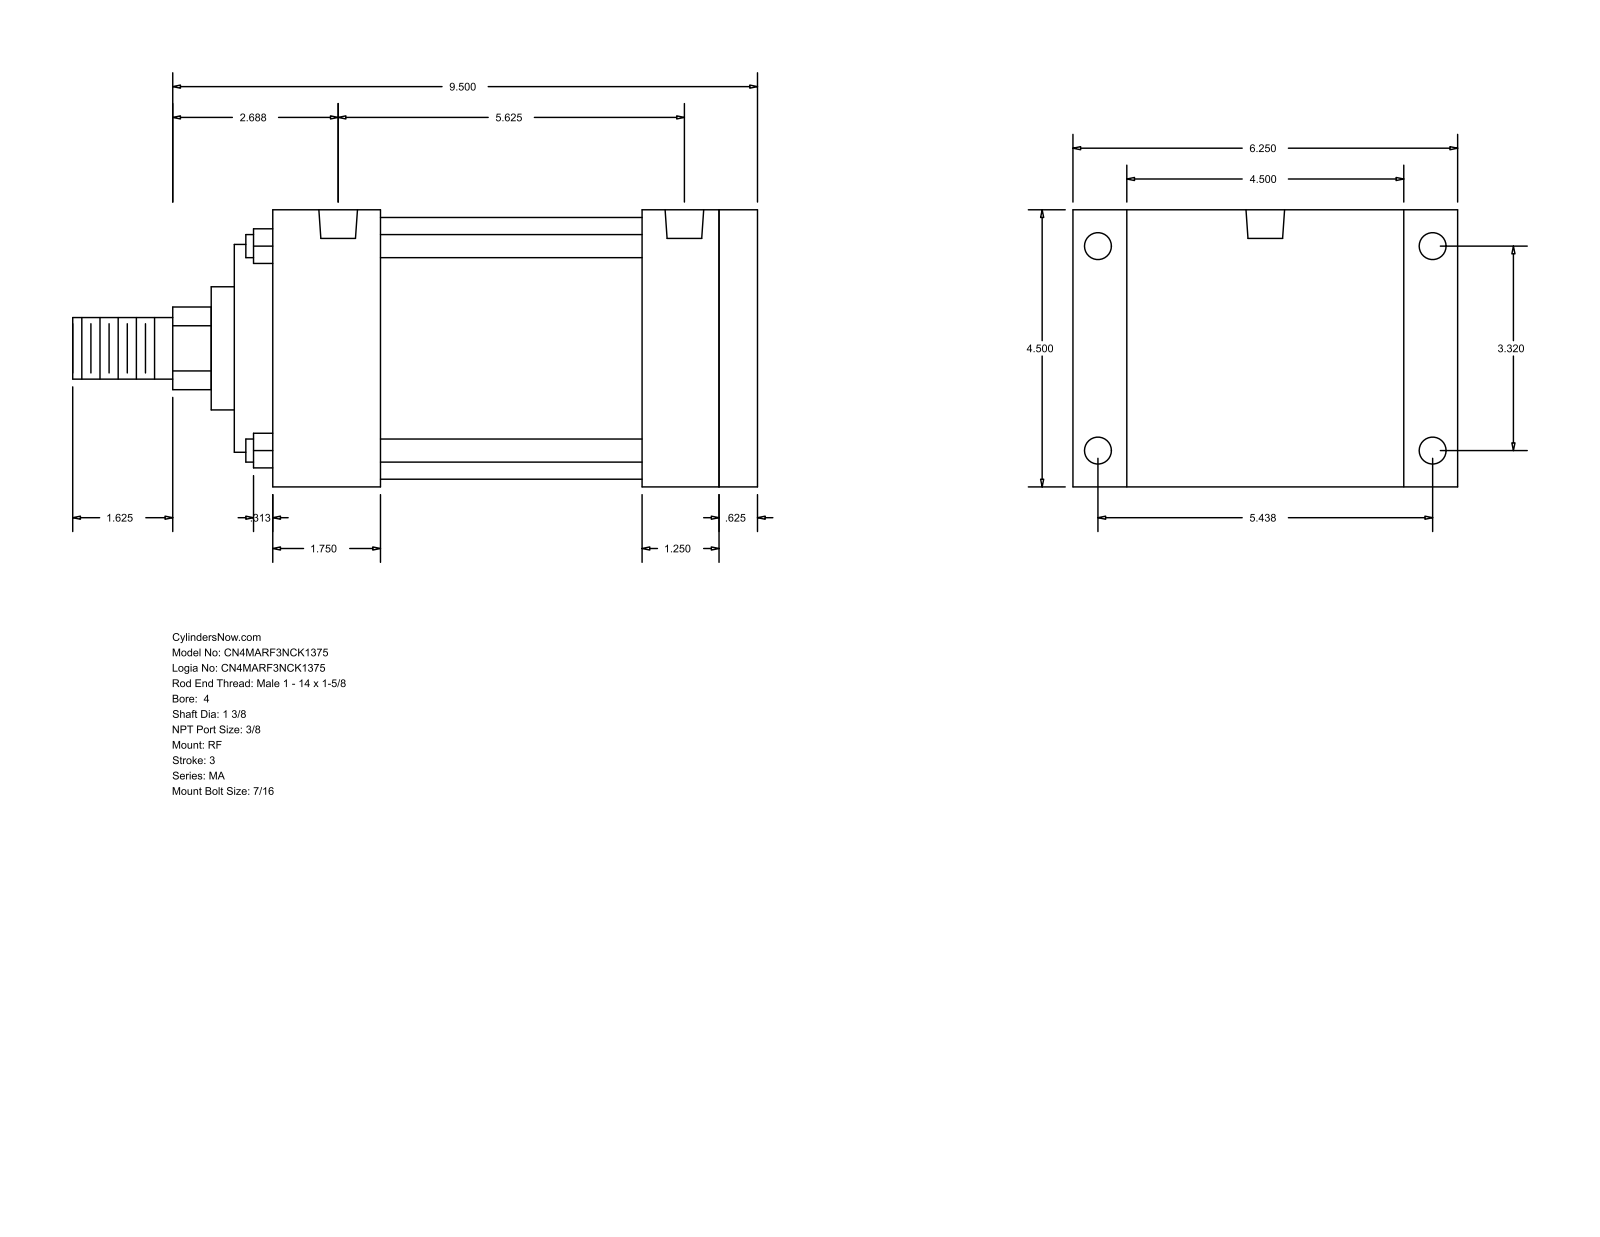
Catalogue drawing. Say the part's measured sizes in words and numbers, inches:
The part is named "MA_RF__0400_1.375". Its 3-D file was written by "GSSL Pune (CONFIG_CONTROL_DESIGN)". It is 0 solids with 94 faces: 65 planar, 29 cylindrical and 0 other. Overall it measures 11.125 by 6.25 by 4.5 inches. Round holes: 8 of diameter 0.437, 2 of diameter 0.627. Round bosses or shafts: 4 of diameter 0.375, 1 of diameter 4.25, 1 of diameter 3.375, 1 of diameter 2, 1 of diameter 1.375, 1 of diameter 1. Partial cylindrical surfaces (rounded edges, fillets, slot ends): 1 of radius 0.672. The main face-to-face distances are 4.5, 7.875, 0.625, 7.25, 8.5, 0.875, 5.375, 6.625, 6, 1.25. The hole center spacings are 5.438, 3.32, 5.25, 6.371, 0.187, 0.188, 5.437, 5.625.
